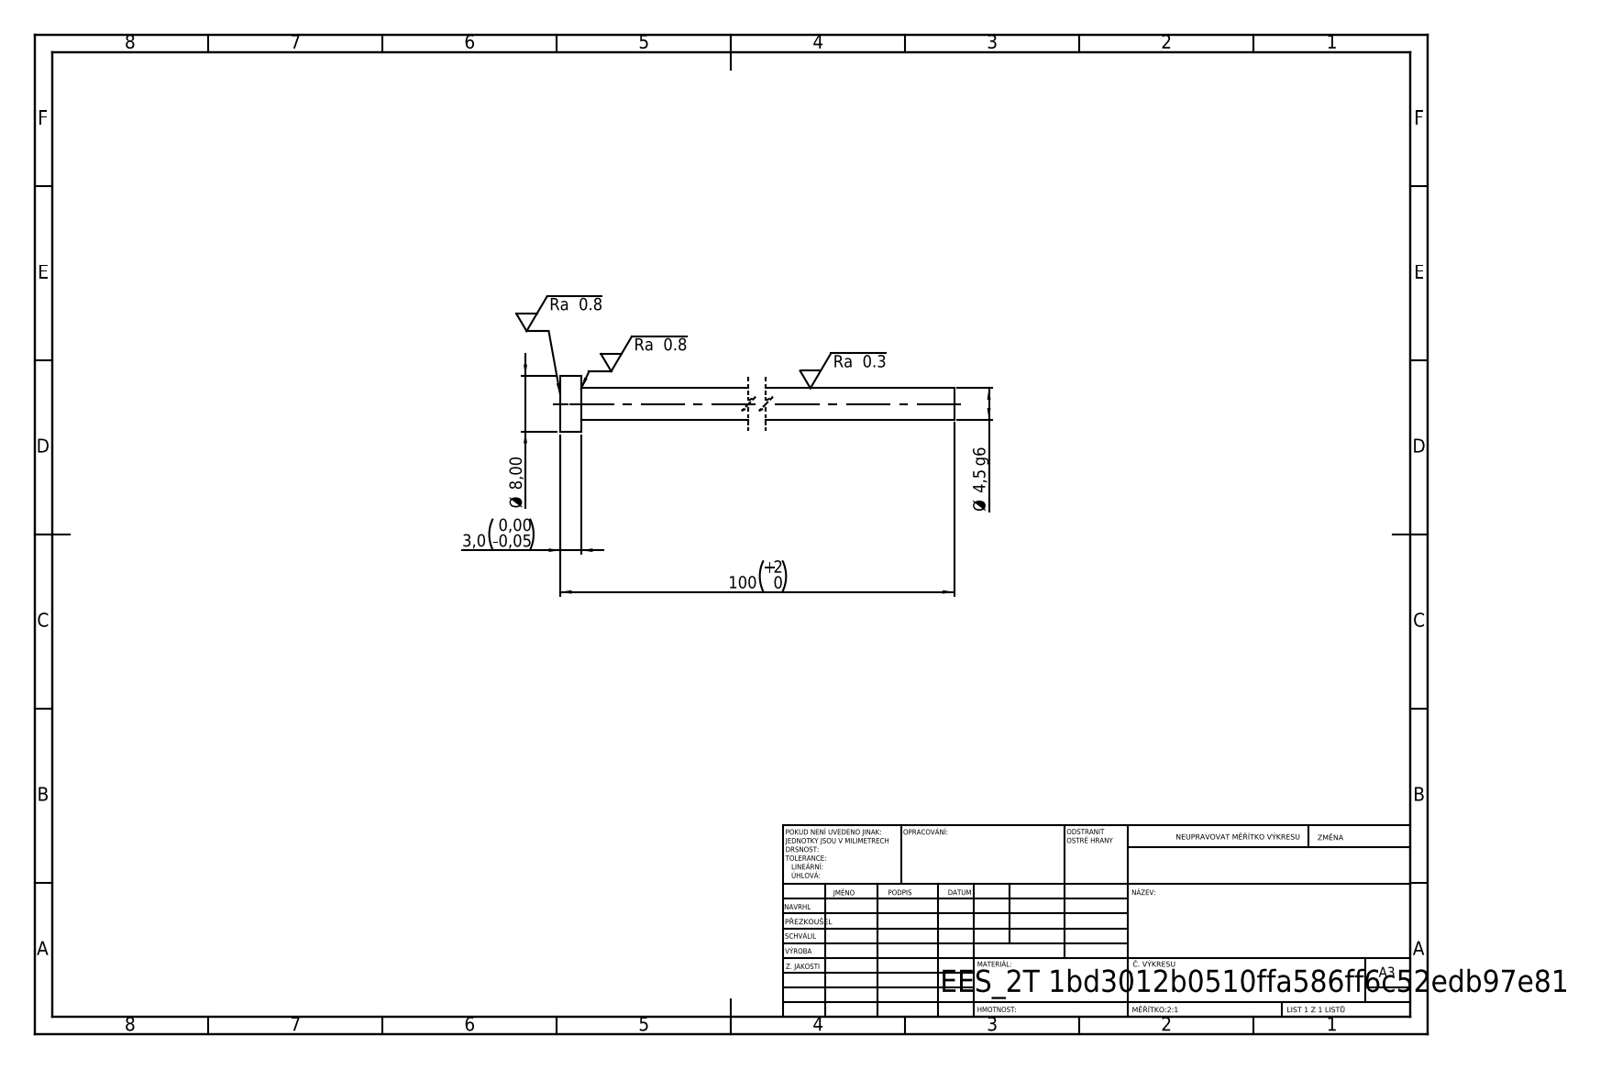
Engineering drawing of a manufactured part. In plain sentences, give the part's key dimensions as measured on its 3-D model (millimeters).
Its 3-D file was written by "SolidWorks 2019 (CONFIG_CONTROL_DESIGN)". It is 1 solid with 7 faces: 3 planar, 4 cylindrical and 0 other. Overall it measures 100 by 8 by 8 millimeters. Its volume is 1 694 cubic millimeters and its surface area 1 547 square millimeters. Round bosses or shafts: 1 of diameter 8, 1 of diameter 4.5. The main face-to-face distances are 3, 100, 97.
